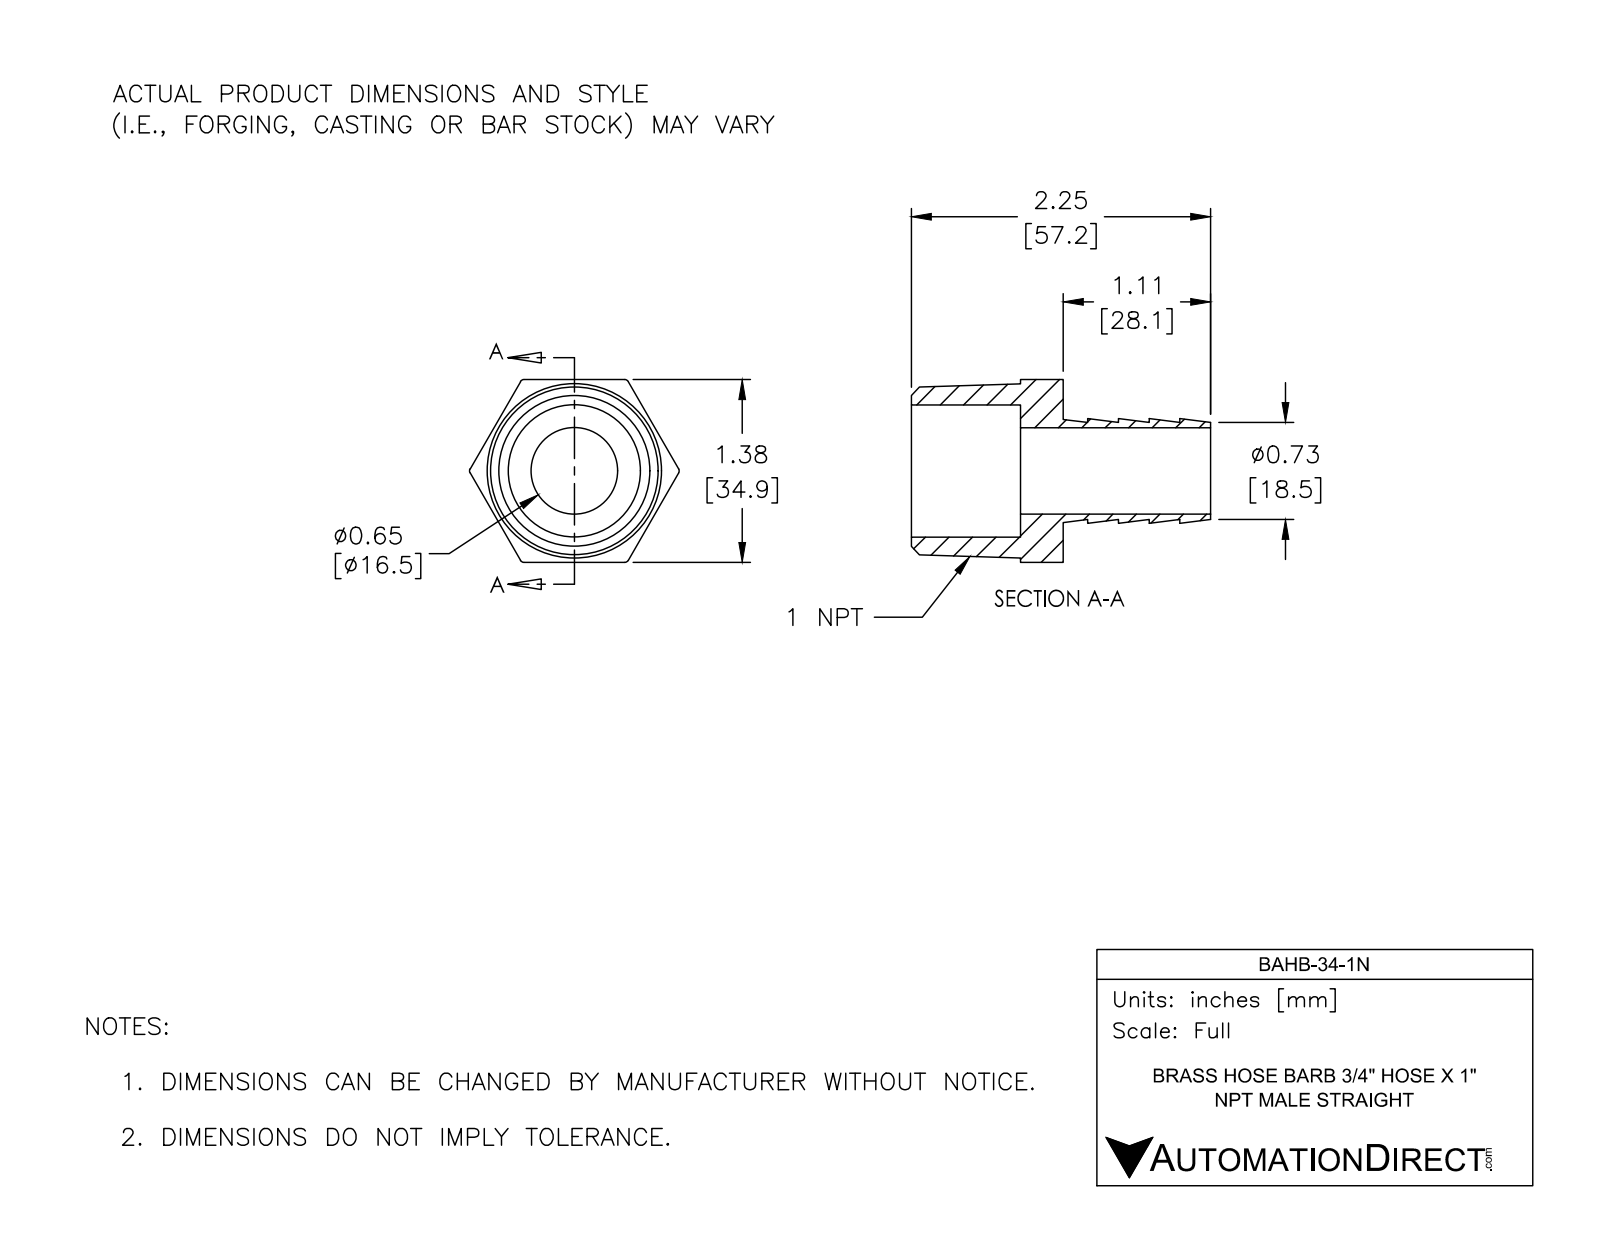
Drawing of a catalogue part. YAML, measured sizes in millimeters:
part_name: "BAHB-34-1N"
step_written_by: "SolidWorks 2017 (AUTOMOTIVE_DESIGN)"
units: millimeters
bodies: {solids: 1, faces: 39, planar: 15, cylindrical: 10, other: 14}
overall_size: [57.2, 40.1, 34.9]
volume: 15900
surface_area: 10050
round_holes:
  - {diameter: 16.5, count: 1}
  - {diameter: 25.2, count: 1}
partial_cylinders:
  - {radius: 0.8, count: 6}
face_to_face_distances: [34.9, 8.2, 29, 20.9, 5.9, 11.7, 28.1, 36.3, 57.2, 5.9]
